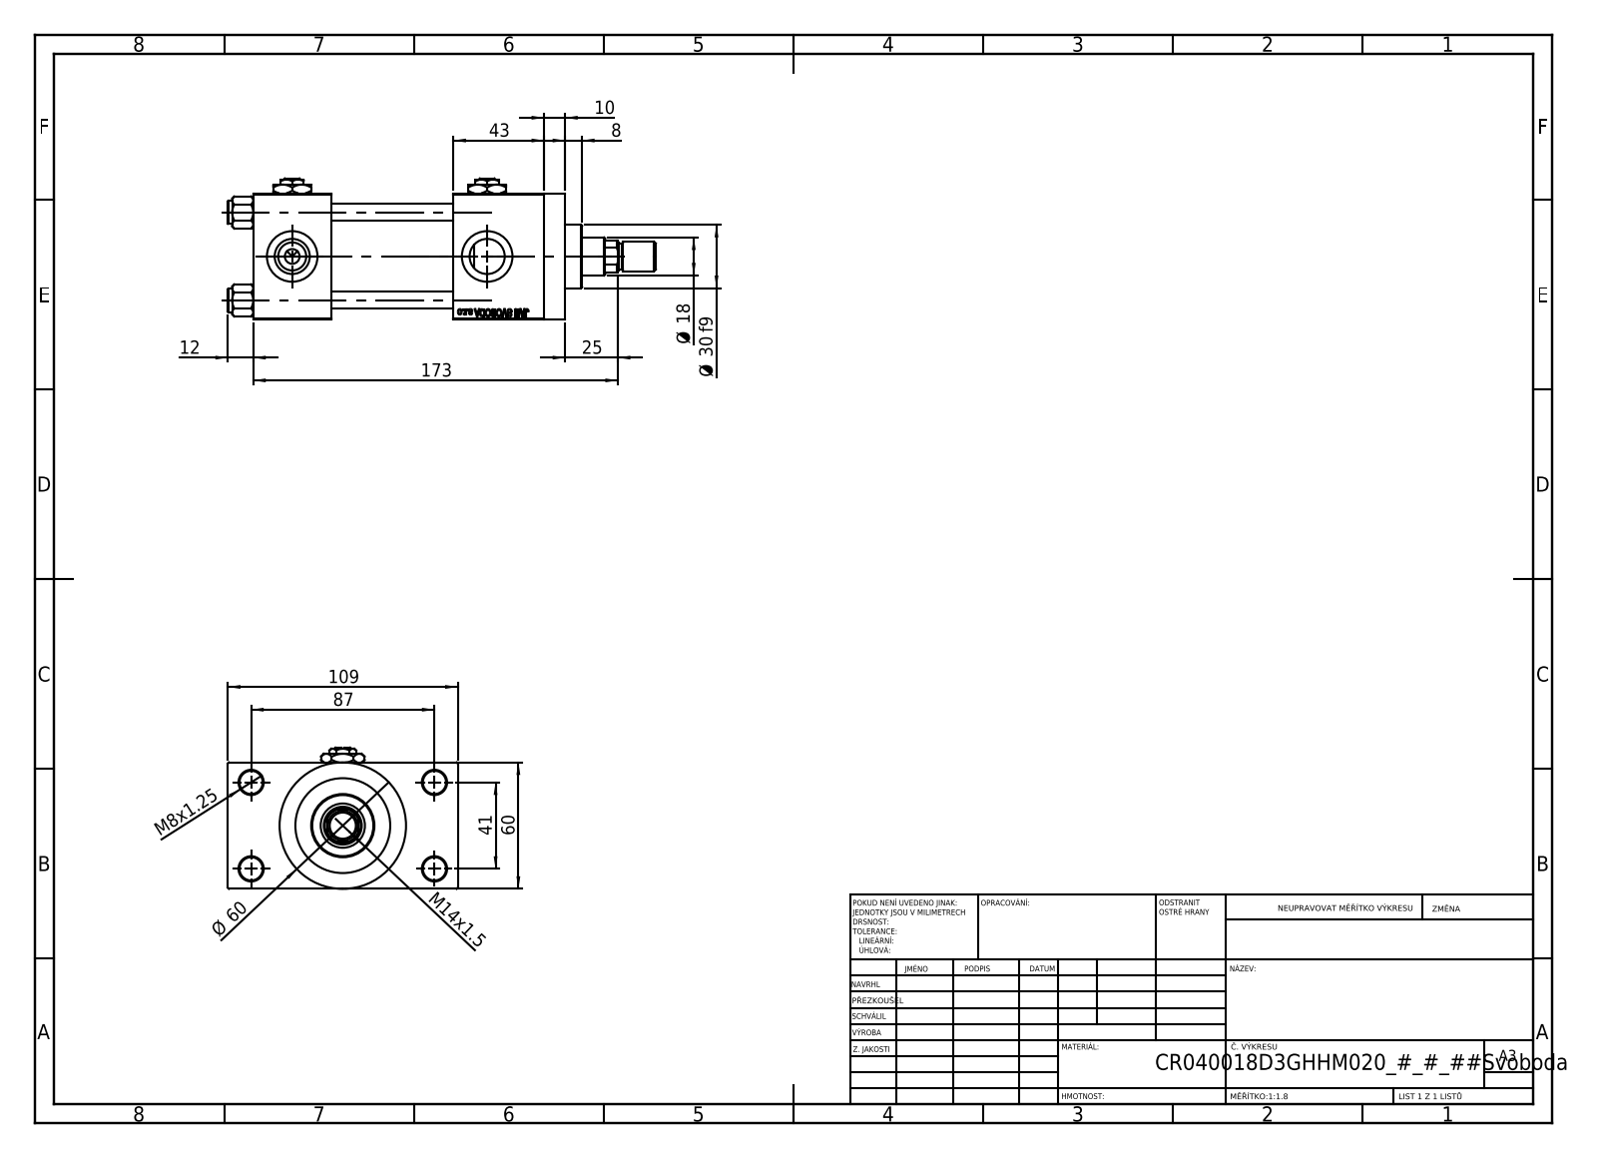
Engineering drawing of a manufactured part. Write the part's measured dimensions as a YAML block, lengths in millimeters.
part_name: "V215CR_D_TYCINKA; V215CR_D_Body; V215_VC_A; ROD_END_AH (+3 more)"
step_written_by: "SolidWorks 2019 (CONFIG_CONTROL_DESIGN)"
units: millimeters
bodies: {solids: 14, faces: 1219, planar: 550, cylindrical: 103, other: 566}
overall_size: [203, 109, 67]
volume: 513009
surface_area: 126318
round_holes:
  - {diameter: 8, count: 4}
  - {diameter: 11, count: 4}
  - {diameter: 16.66, count: 4}
  - {diameter: 24, count: 4}
  - {diameter: 7, count: 3}
  - {diameter: 8.5, count: 1}
  - {diameter: 18, count: 1}
  - {diameter: 21, count: 1}
  - {diameter: 31, count: 1}
  - {diameter: 40, count: 1}
  - {diameter: 45, count: 1}
round_bosses_or_shafts:
  - {diameter: 11, count: 4}
  - {diameter: 60, count: 1}
  - {diameter: 46, count: 1}
  - {diameter: 30, count: 1}
  - {diameter: 14, count: 1}
  - {diameter: 12, count: 1}
partial_cylinders:
  - {radius: 8.5, count: 1}
face_to_face_distances: [60, 58, 24.5, 84.5, 37, 95, 43, 138, 101, 53]
hole_center_spacings: [22.65, 29.49, 41.7, 47.15, 48.09, 64.35, 76.49, 41]
